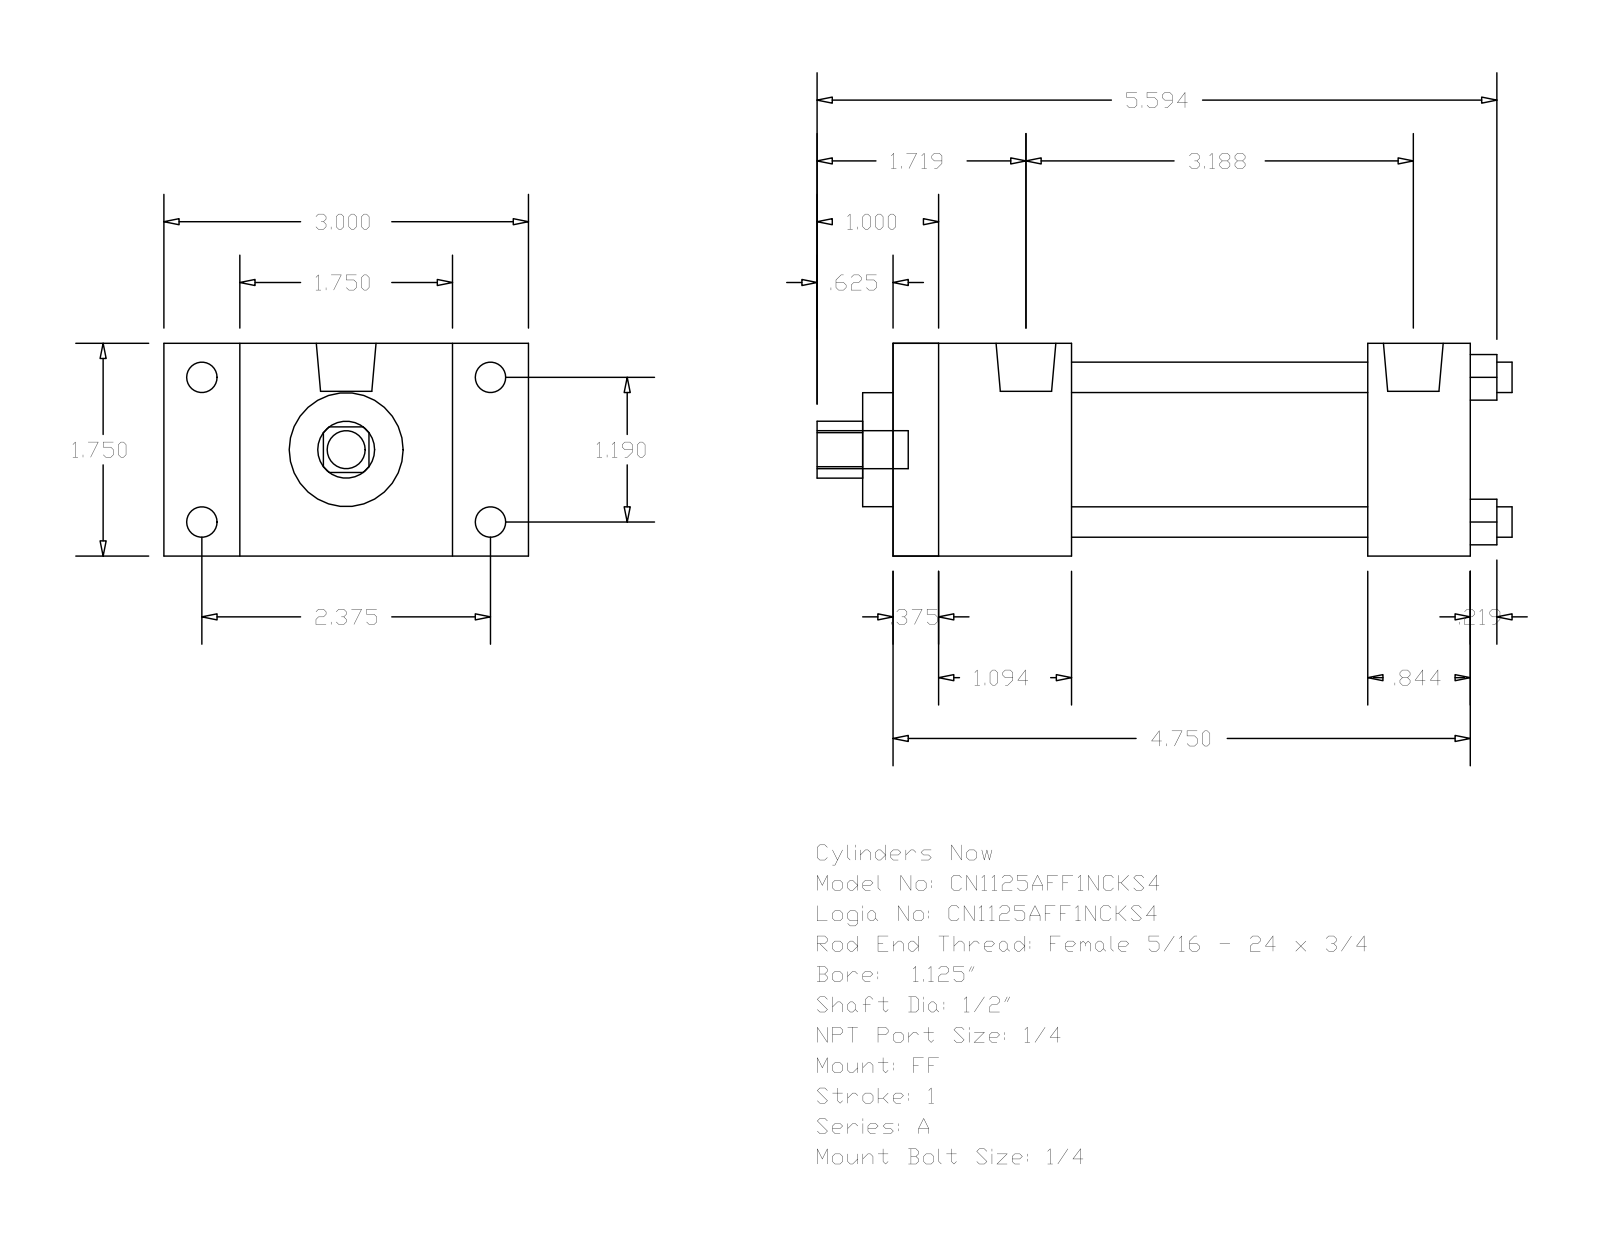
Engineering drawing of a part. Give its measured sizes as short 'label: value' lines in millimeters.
name: A_FF__0112_0.5
written by: GSSL Pune (CONFIG_CONTROL_DESIGN)
unit: mm
bodies: 0 solids, 92 faces (64 planar, 28 cylindrical, 0 other)
size: 145.26 × 76.2 × 44.45
holes: 4× ⌀6.35, 1× ⌀12.7, 1× ⌀23.81, 1× ⌀31.88
bosses: 4× ⌀6.35, 4× ⌀5.56, 2× ⌀12.49, 1× ⌀7.94
rounds: 1× R5.94
face distances: 44.46, 120.65, 9.52, 111.13, 15.87, 99.21, 89.69, 21.44, 37.3, 27.78
hole spacings: 21.37, 30.22, 42.74
